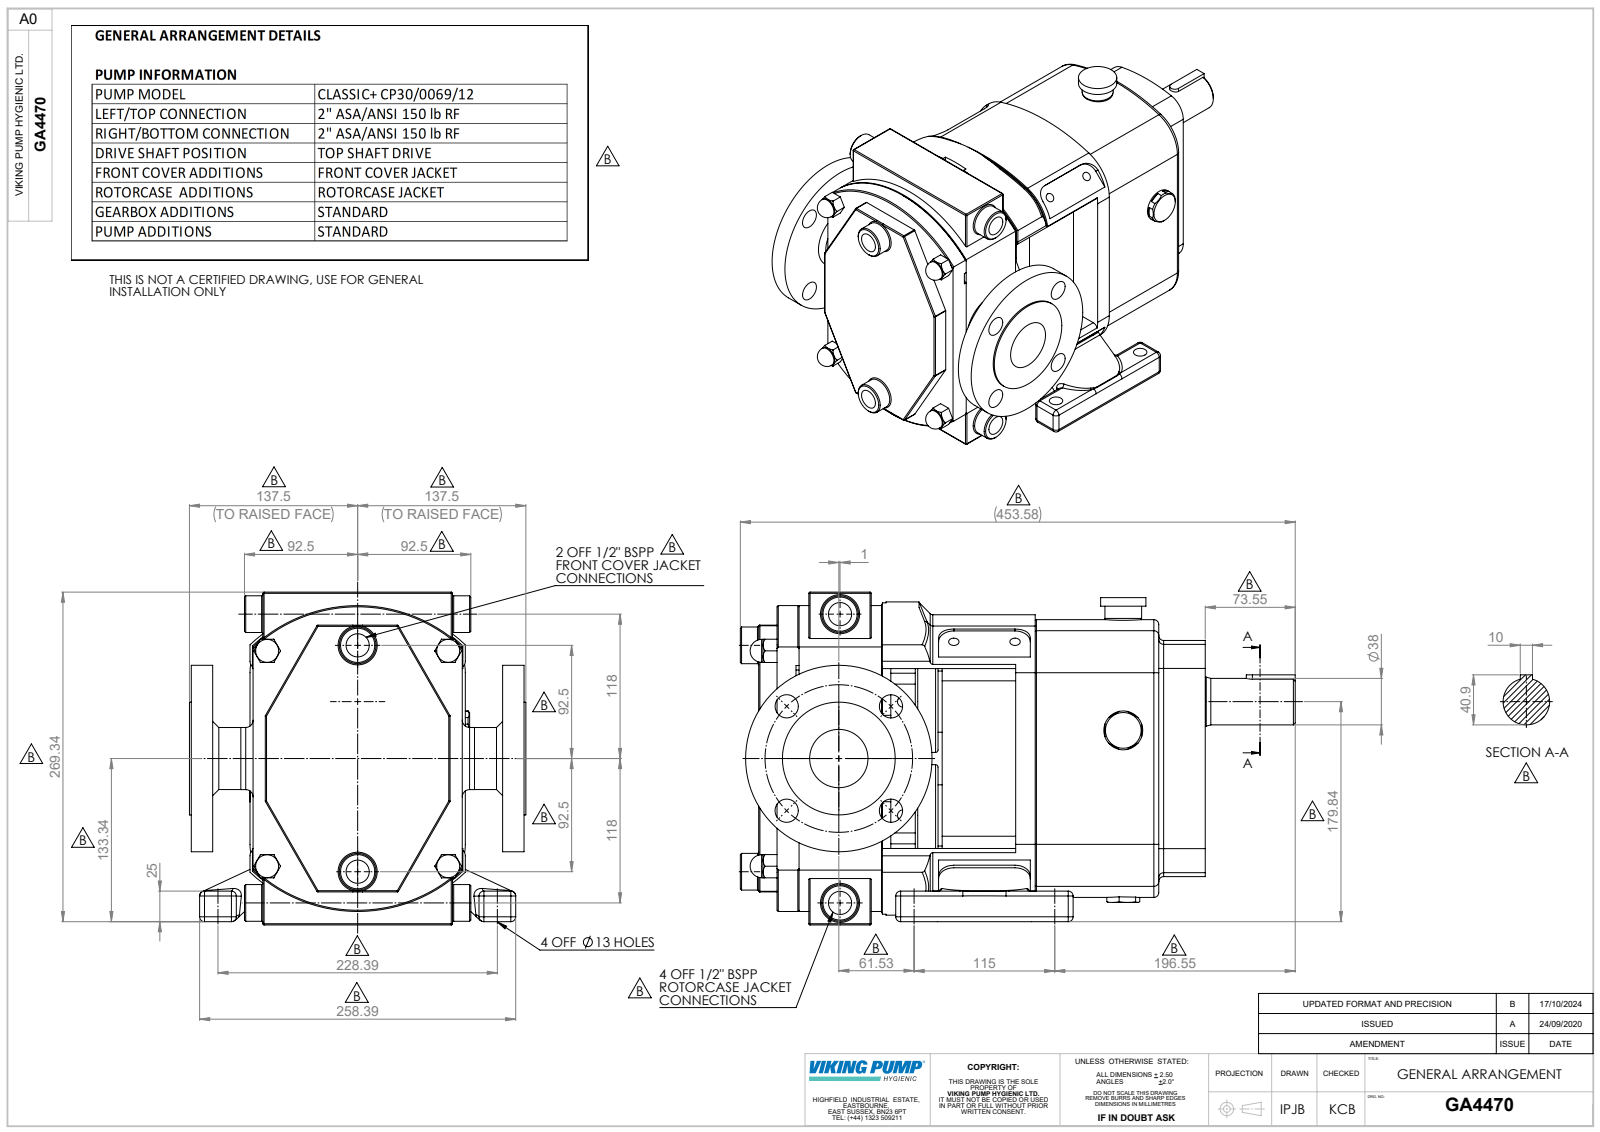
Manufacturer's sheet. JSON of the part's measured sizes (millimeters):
{"part_name": "Copy of CP30-0069-12 H T^GA4470; Copy of MP30 Half Inch BSP Jacket^GA4470; Copy of MP30S Half Inch Jacket^GA4470; Copy of Z94-5301-33 - 2 INCH ASA 150^GA4470 (+1 more)", "step_written_by": "SolidWorks 2023 (AUTOMOTIVE_DESIGN)", "units": "millimeters", "bodies": {"solids": 6, "faces": 870, "planar": 295, "cylindrical": 318, "other": 257}, "overall_size": [453.58, 275, 272], "volume_mm3": 12740000, "surface_area_mm2": 737467, "round_holes": [[19, 6], [8.5, 4], [10.11, 4], [13, 4], [18.97, 4], [9.09, 2], [35, 1], [47.7, 1]], "round_bosses_or_shafts": [[30, 5], [18.8, 4], [83, 2], [50, 2], [152.4, 1], [92.2, 1], [50.8, 1], [50.7, 1]], "partial_cylinders_radius": [[1, 44], [4, 44], [10, 12], [6, 10], [12.5, 4], [12.57, 4], [12.6, 4], [20, 4]], "face_to_face_distances": [1.5, 33, 52, 221.5, 204, 34.5, 202.5, 169.5, 15, 30.5], "hole_center_spacings": [60.3, 63.64, 85.28, 120.6, 130.37, 10.59, 34.84, 50.05]}
